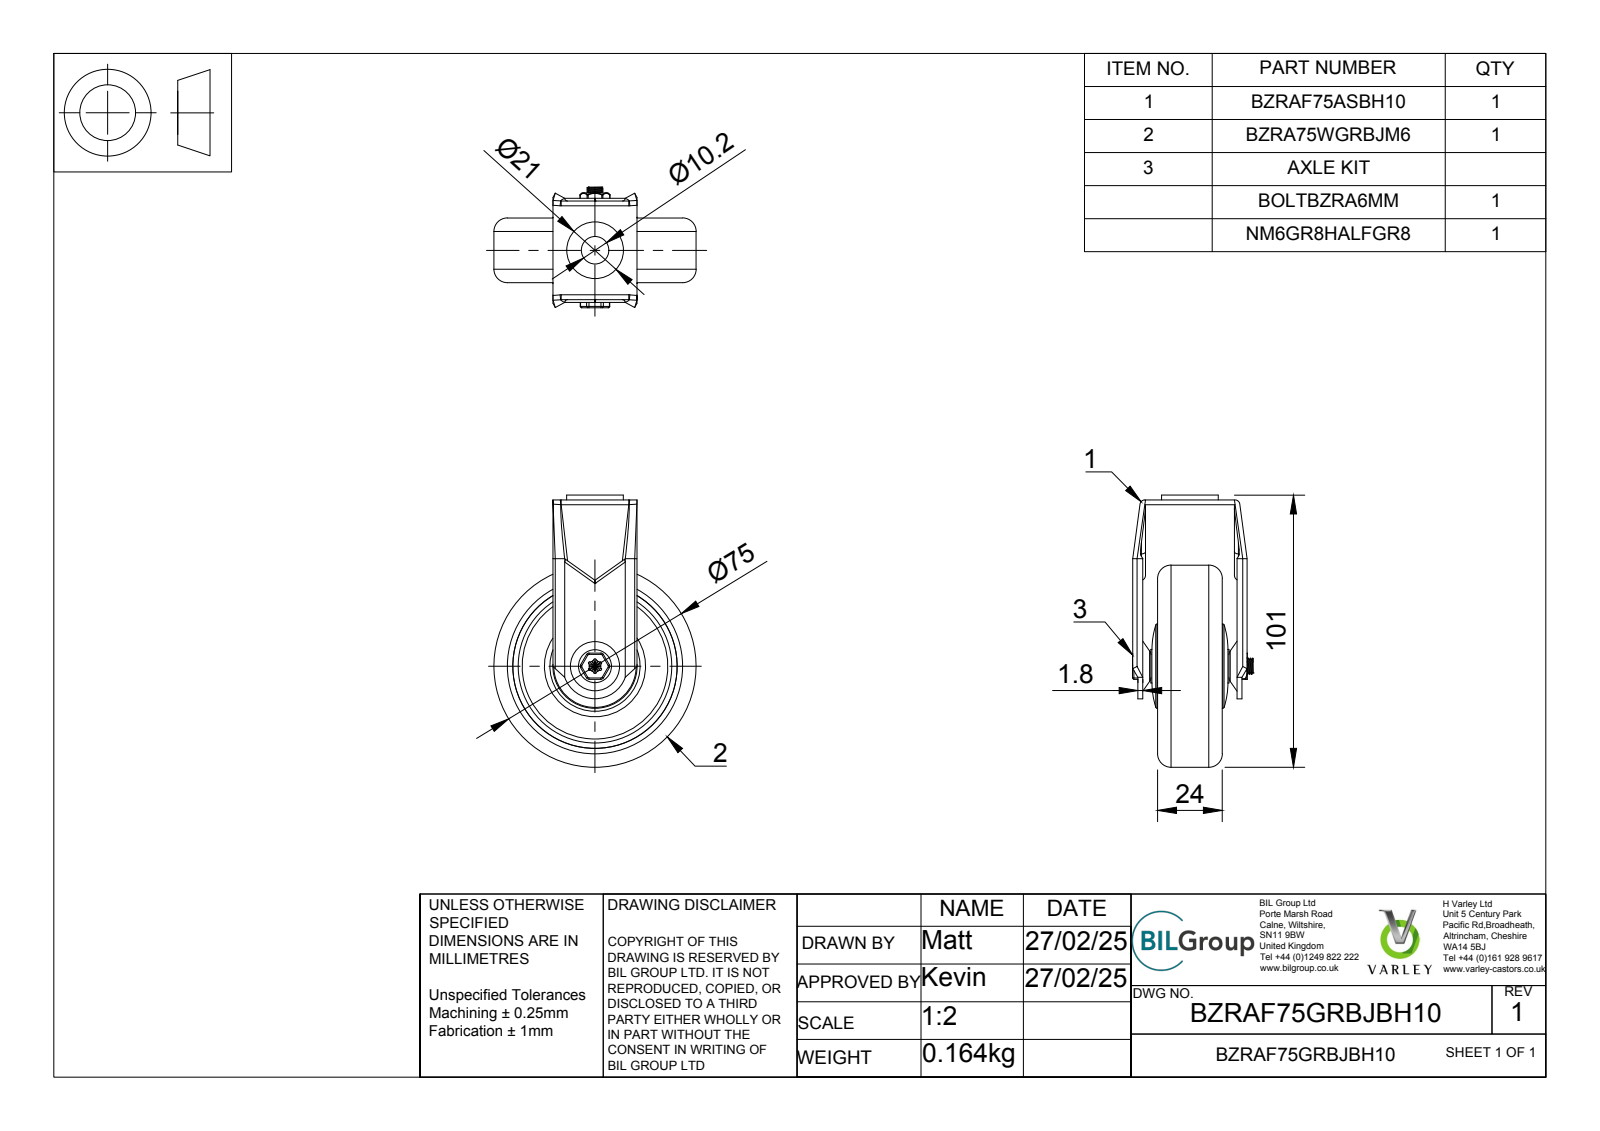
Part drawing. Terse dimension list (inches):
name: BZRAF75GRBJBH10 v2; BZRAF75ASBH10 v1; ZINC PLATED PRESSED STEEL FORKS; BZRA75WGRBJM6 v1 (+7 more)
written by: Autodesk Translation Framework v13.20.0.188 (AP242_MANAGED_MODEL_BASED_3D_ENGINEERING_MIM_LF)
unit: in
bodies: 18 solids, 396 faces (117 planar, 134 cylindrical, 145 other)
size: 3.976 × 2.953 × 1.772
volume: 4.525 in³; area: 82.97 in²
holes: 1× ⌀0.236, 1× ⌀0.24, 1× ⌀0.244, 1× ⌀0.268, 1× ⌀0.315, 1× ⌀0.323, 1× ⌀0.402, 1× ⌀0.415, 1× ⌀0.441, 1× ⌀0.502, 1× ⌀0.72, 1× ⌀0.756
bosses: 1× ⌀2.953, 1× ⌀1.476, 1× ⌀1.23, 1× ⌀1.102, 1× ⌀0.827, 1× ⌀0.736, 1× ⌀0.721, 1× ⌀0.492
rounds: 26× R0.039, 12× R0.02, 8× R0.059, 6× R0.016, 4× R0.039, 2× R0.071, 1× R0.083, 1× R0.469
face distances: 0.071, 0.433, 0.512, 0.039, 1.409, 0.177, 0.344, 0.61, 0.167, 0.217
